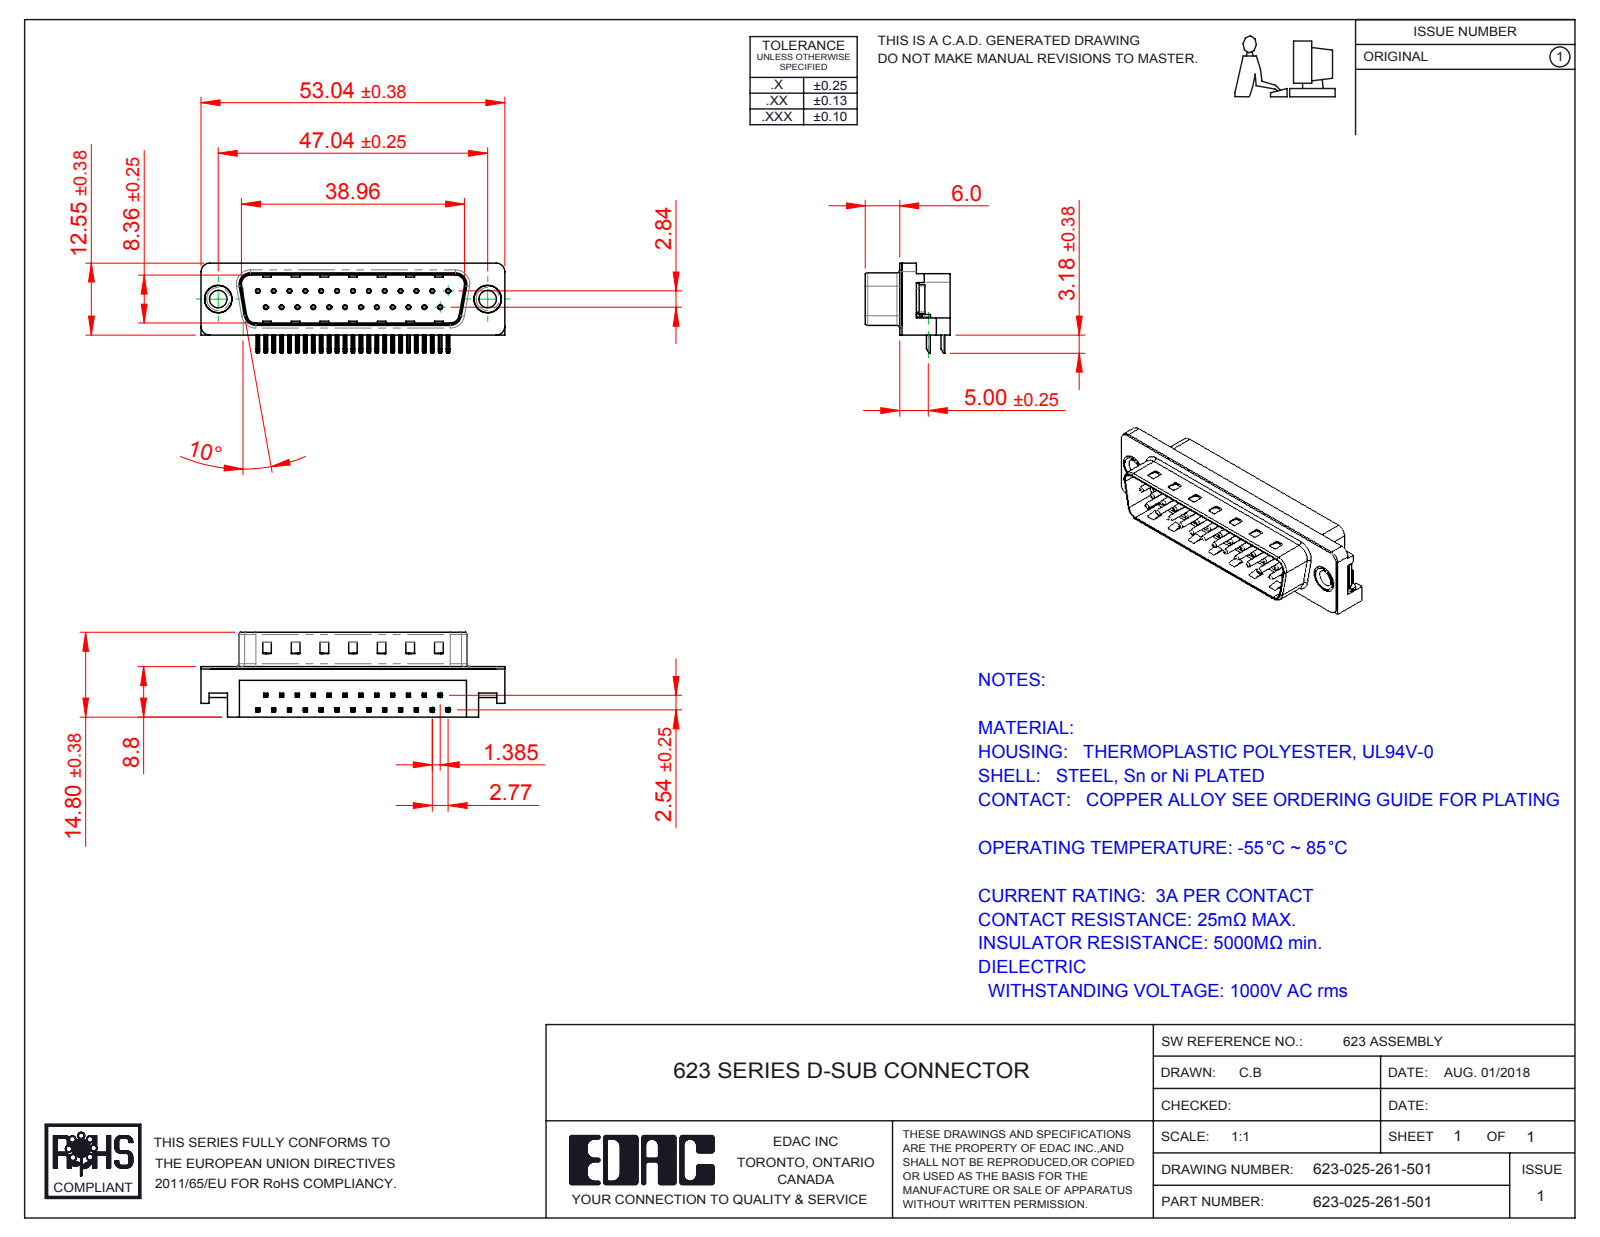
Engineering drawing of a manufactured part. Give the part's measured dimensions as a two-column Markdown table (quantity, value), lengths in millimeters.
| quantity | value |
| --- | --- |
| part name | 623 Contact Bottom; 623-025-261-501; 623 Housing_25 Socket; 623 Non Board Mount (+3 more) |
| STEP written by | SolidWorks 2016 (CONFIG_CONTROL_DESIGN) |
| units | millimeters |
| bodies | 31 solids, 2213 faces (1405 planar, 631 cylindrical, 177 other) |
| overall size | 53.04 × 15.73 × 14.8 |
| volume | 4 712 mm³ |
| surface area | 6 693 mm² |
| round holes (diameter × count) | 0.35 × 25, 0.8 × 25, 3.05 × 2, 4 × 2, 4.8 × 2, 5 × 2 |
| round bosses / shafts (diameter × count) | 0.75 × 25, 4.9 × 2, 4.75 × 2, 3.85 × 2 |
| partial cylindrical surfaces (radius × count) | 0.25 × 108, 0.12 × 50, 1 × 16, 0.5 × 9, 1.5 × 7, 0.9 × 4, 1.6 × 4, 2 × 4 |
| main face-to-face distances | 0.4, 8.4, 2.1, 1.7, 8.76, 10.46, 10.86, 10.35, 8.8, 5.9 |
| hole center spacings | 3.16, 2.77, 11.08, 5.54, 8.31, 5.03, 13.85, 7.48 |
